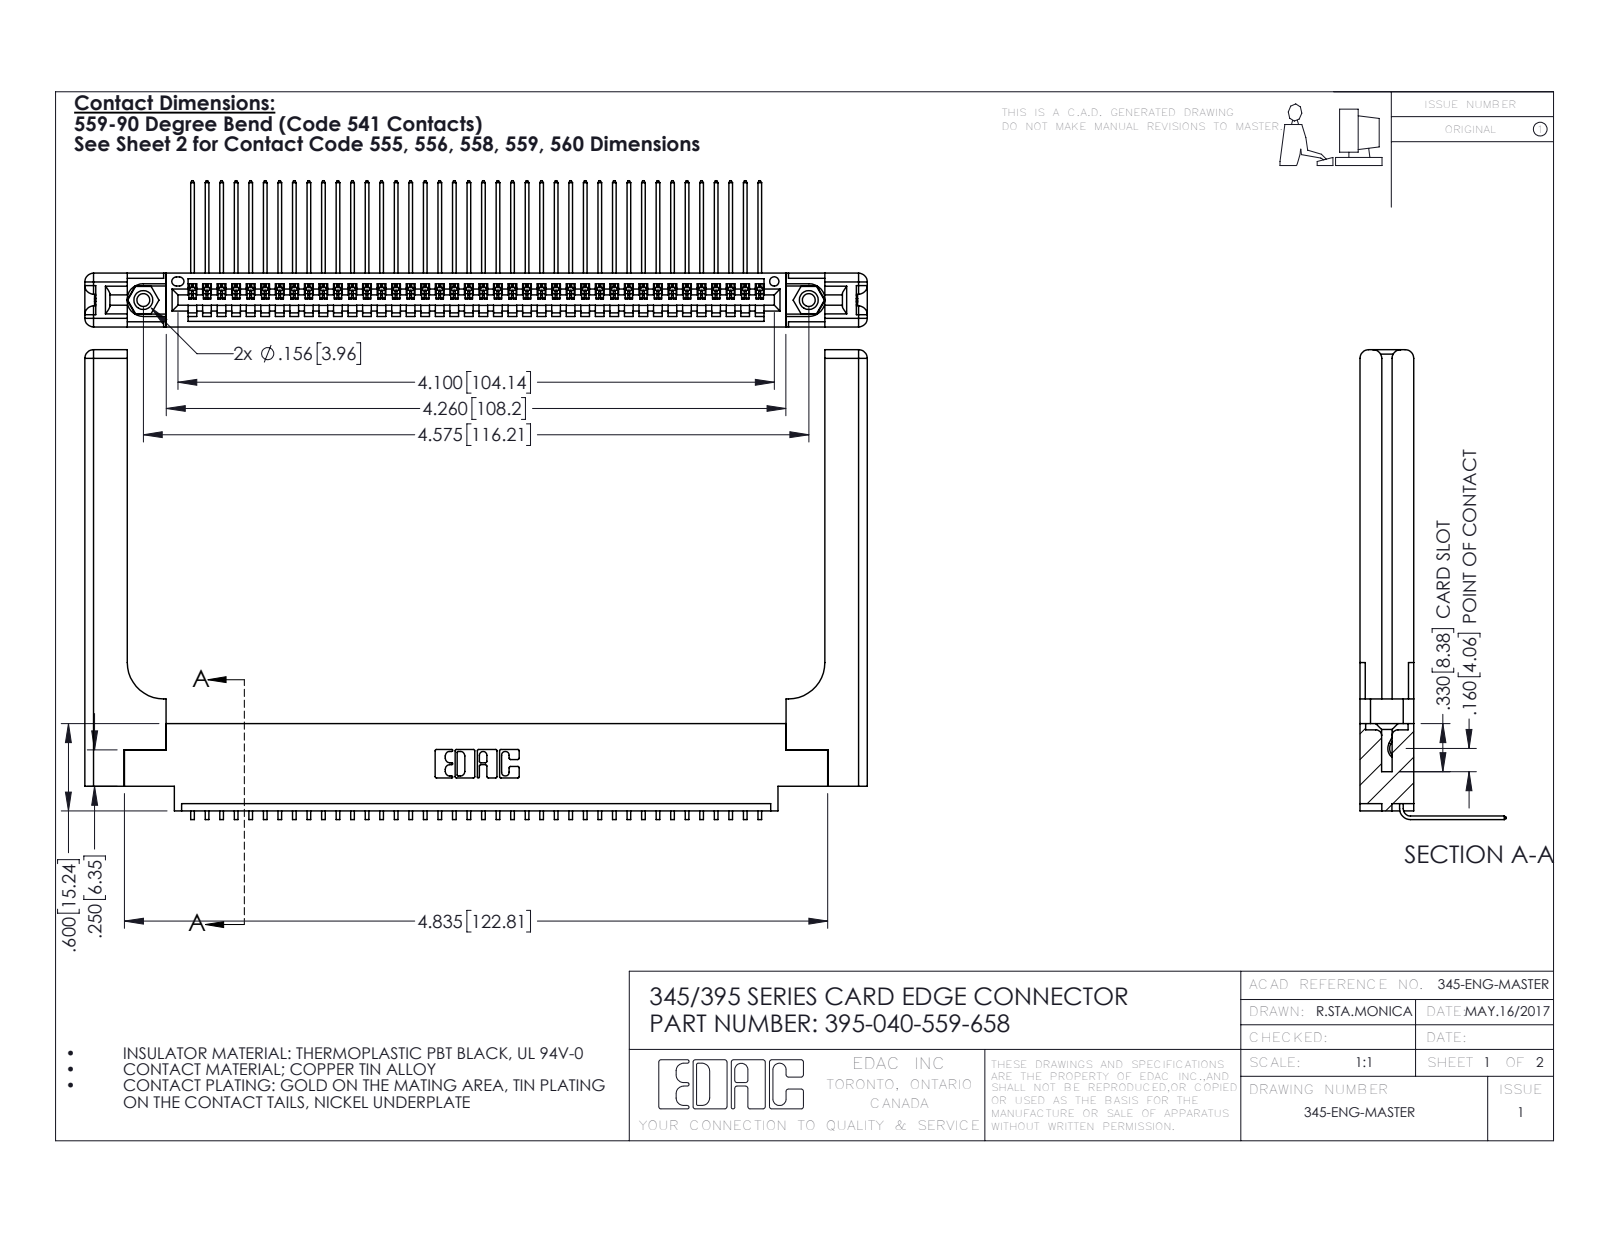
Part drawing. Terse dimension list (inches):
name: 345-292-001_558 559 Tail - 1; 395-040-559-658; 345-220-058_345-220-058; 345-250-001_345-250-001-102 (+1 more)
written by: SolidWorks 2016 (CONFIG_CONTROL_DESIGN)
unit: in
bodies: 45 solids, 2786 faces (1912 planar, 814 cylindrical, 60 other)
size: 5.379 × 3.229 × 1.005
volume: 1.311 in³; area: 36.33 in²
holes: 2× ⌀0.089, 2× ⌀0.125, 2× ⌀0.156, 1× ⌀0.064
bosses: 2× ⌀0.155
rounds: 80× R0.006, 22× R0.01, 16× R0.06, 6× R0.007, 6× R0.031, 3× R0.026, 2× R0.03, 2× R0.031
face distances: 0.37, 0.072, 0.298, 0.098, 0.272, 0.025, 0.2, 0.148, 0.15, 0.225
hole spacings: 0.27, 4.339, 4.575
